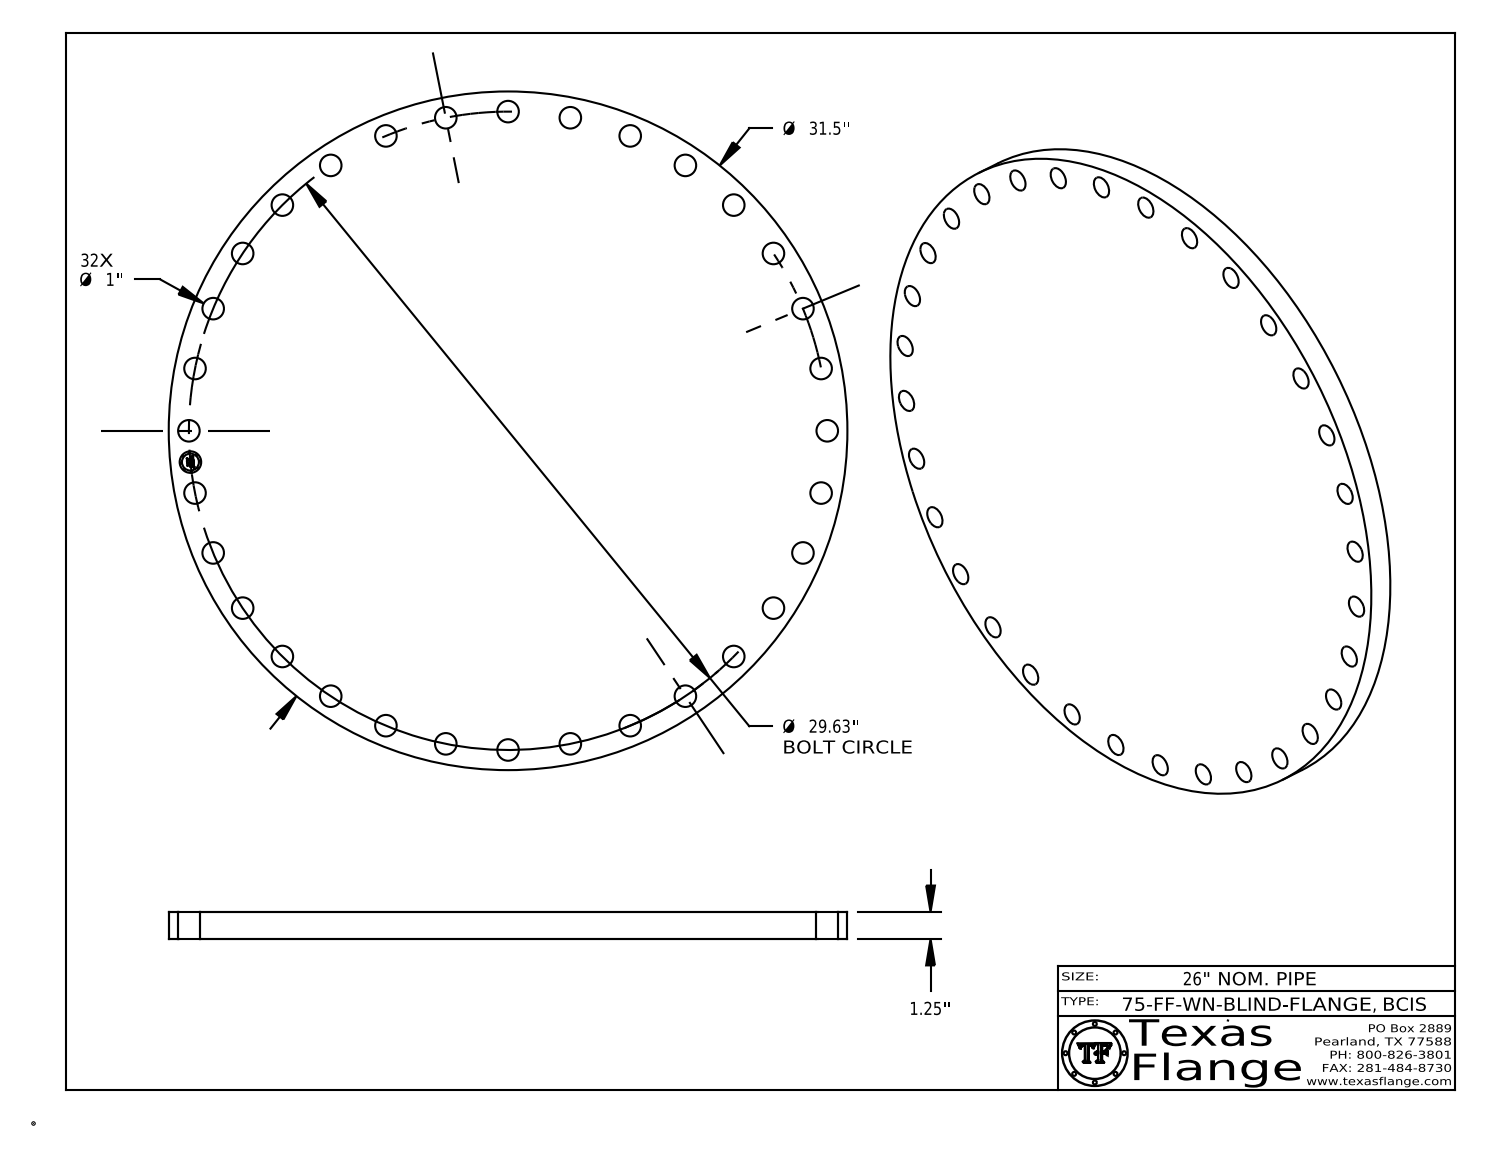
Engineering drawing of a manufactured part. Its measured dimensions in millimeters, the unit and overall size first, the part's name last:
Units: millimetres
Overall size (bounding box): 800.1 × 800.1 × 31.8
Round holes (diameter × count): ⌀25.4 ×33
Round bosses / shafts (diameter × count): ⌀1.5 ×8, ⌀800.1 ×1, ⌀20 ×1
Main face-to-face distances: 31.8, 31.4, 0.4, 7.6, 7.4, 1.4, 4.9, 6.3, 1.1, 3.8
Hole centre spacings: 73.8, 625.8, 532.2, 695.3, 218.5, 354.8, 720.2, 749
Volume: 15 450 000 mm³ · Surface area: 1 134 000 mm²
Bodies: 1 solid, 453 faces (367 planar, 86 cylindrical, 0 other)
Part name (STEP PRODUCT): 75-FF-WN-BLIND, Series BCIS
STEP written by: CATIA V5 STEP AP214 (AUTOMOTIVE_DESIGN)
